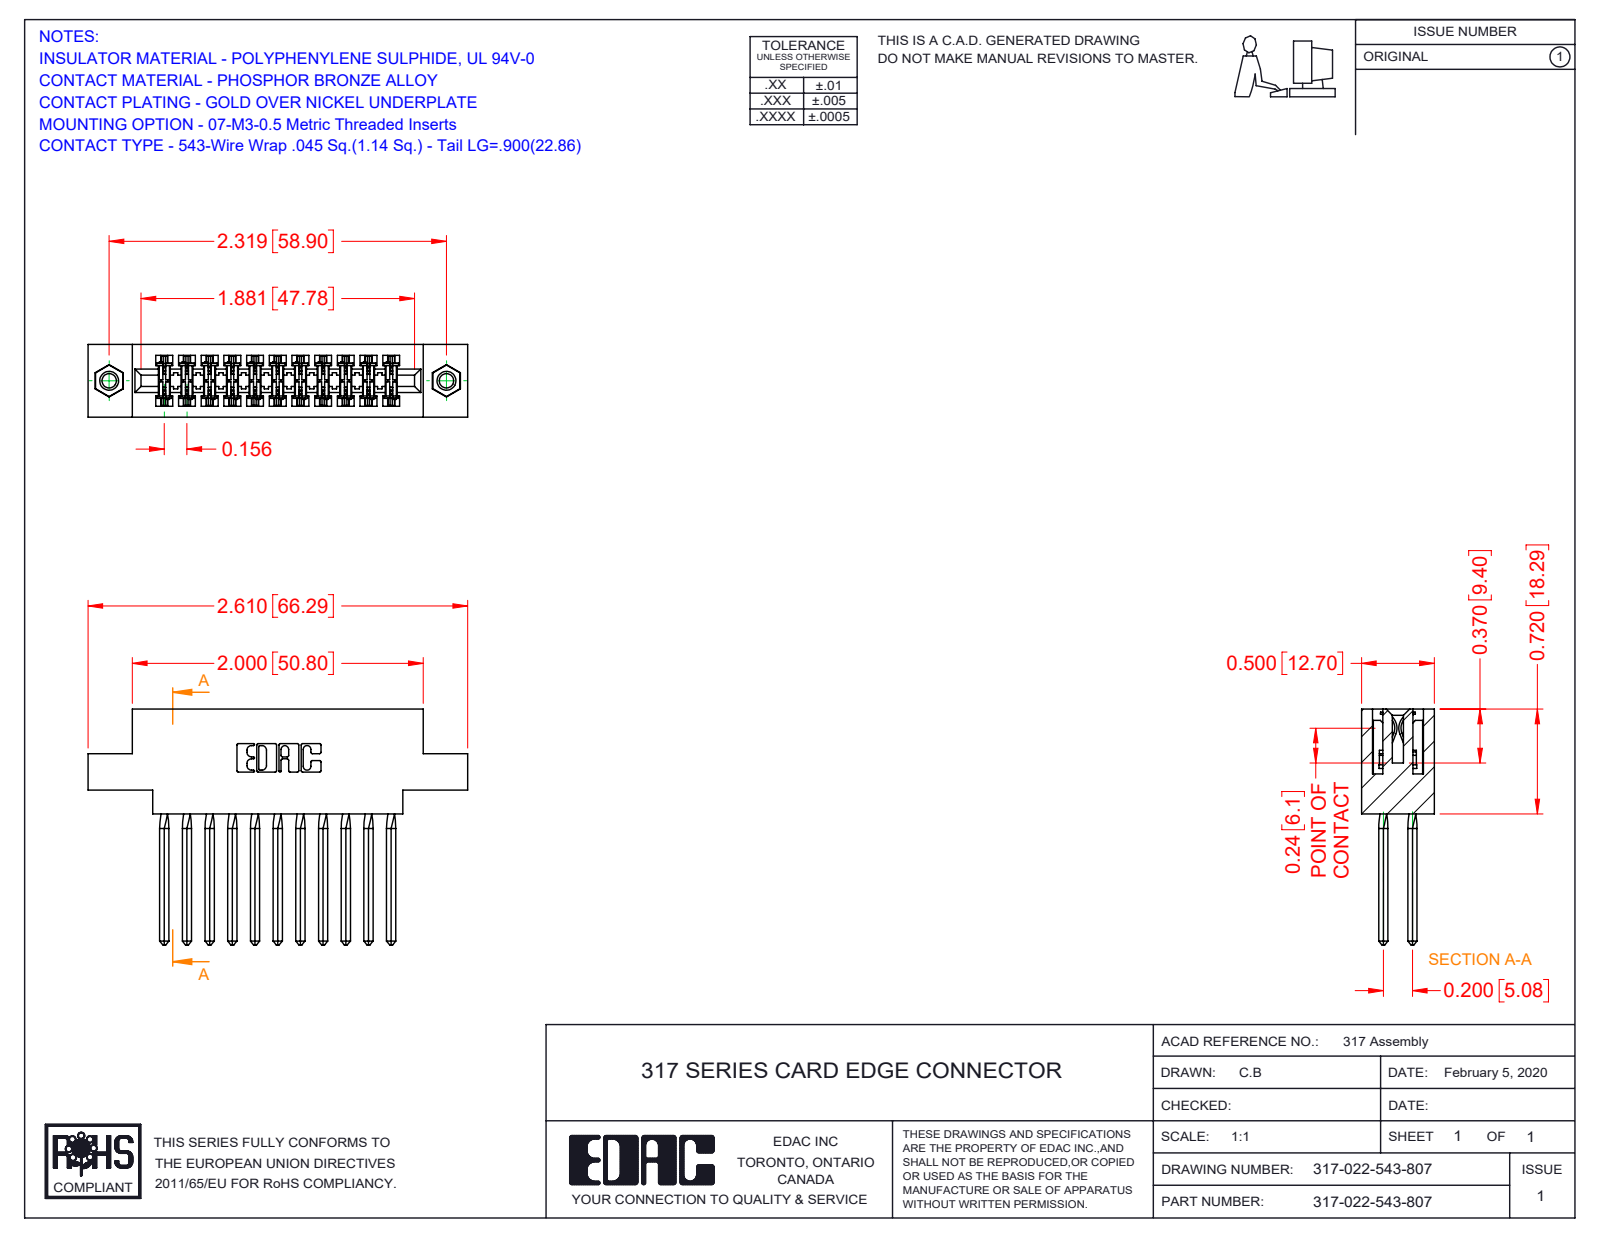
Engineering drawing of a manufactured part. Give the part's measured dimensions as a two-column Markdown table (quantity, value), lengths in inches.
| quantity | value |
| --- | --- |
| part name | 317-022-543-807; 317-290-001_543; 317 Part_.156 Dia - TI; 345-250-001_345-250-005-103 |
| STEP written by | SolidWorks 2016 (CONFIG_CONTROL_DESIGN) |
| units | inches |
| bodies | 25 solids, 2120 faces (1696 planar, 320 cylindrical, 104 other) |
| overall size | 2.61 × 1.62 × 0.5 |
| volume | 0.621 in³ |
| surface area | 22.09 in² |
| round holes (diameter × count) | 0.098 × 2, 0.125 × 2, 0.156 × 2 |
| round bosses / shafts (diameter × count) | 0.155 × 2 |
| partial cylindrical surfaces (radius × count) | 0.015 × 44, 0.01 × 22, 0.007 × 6, 0.031 × 6, 0.026 × 3, 0.095 × 2, 0.1 × 2, 0.11 × 2 |
| main face-to-face distances | 0.5, 0.075, 0.11, 0.425, 0.22, 0.331, 0.35, 0.116, 0.156, 0.136 |
| hole center spacings | 2.319 |
